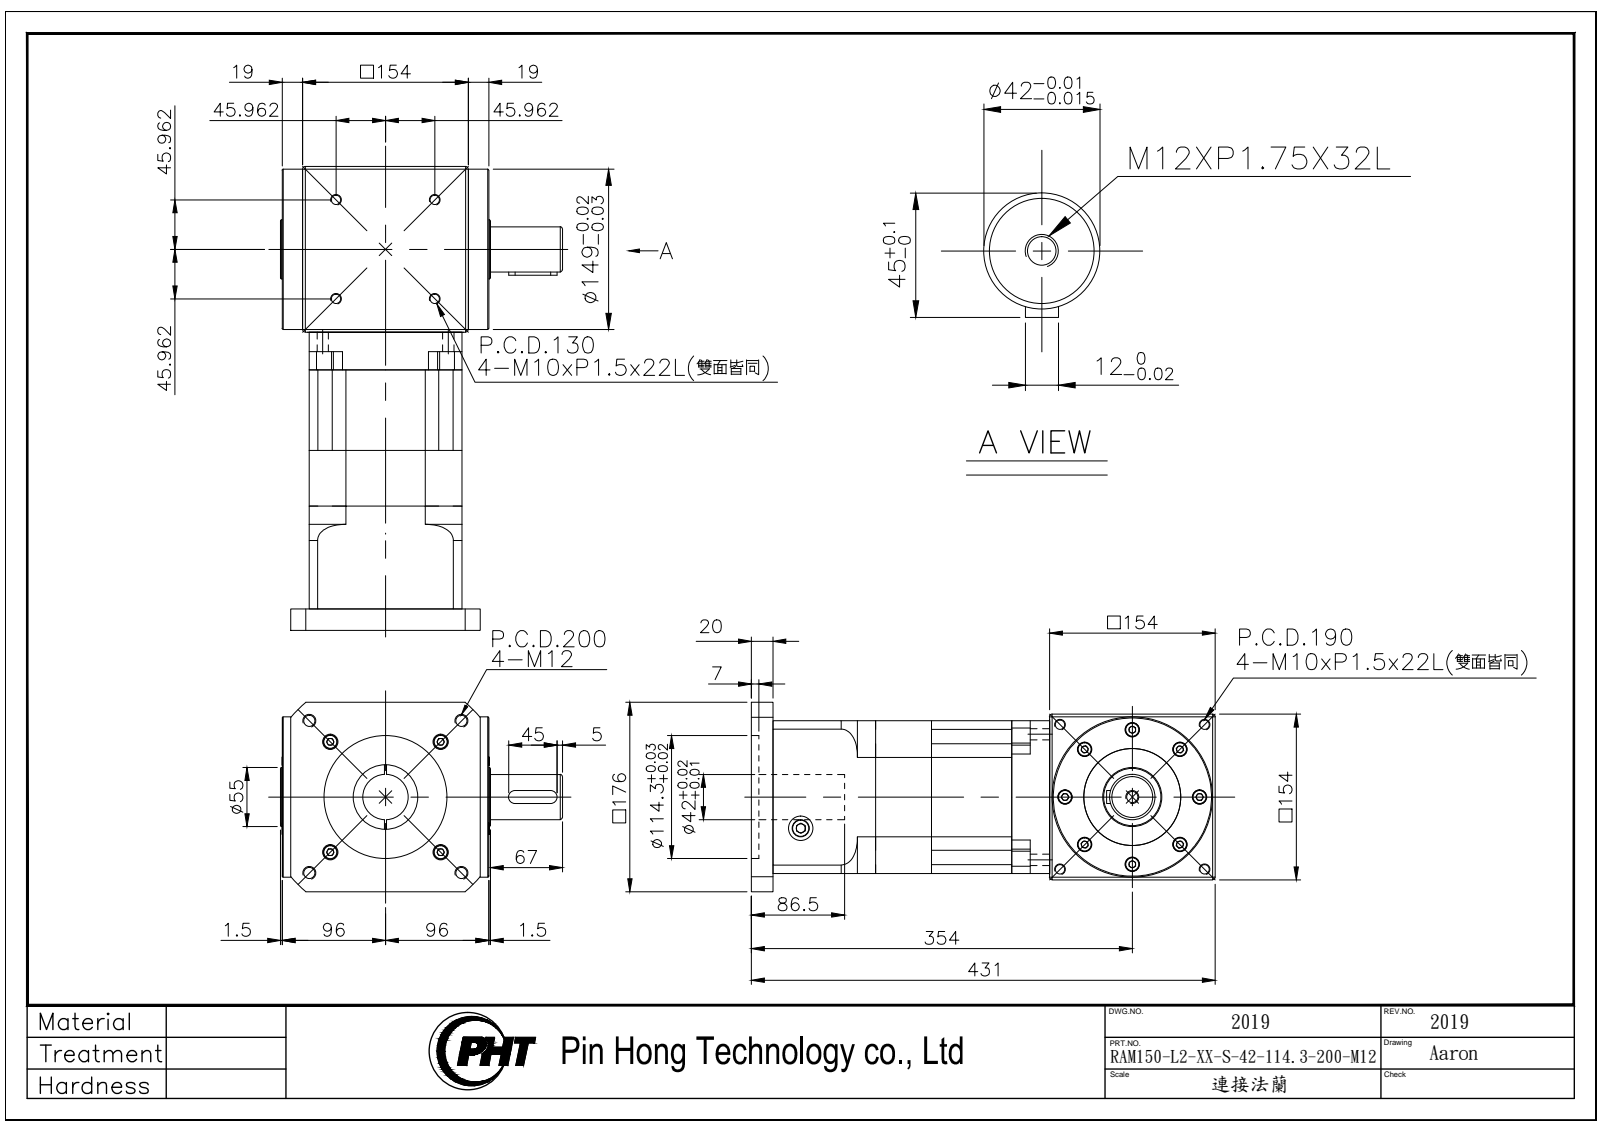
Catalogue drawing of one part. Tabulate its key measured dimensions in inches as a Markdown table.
| quantity | value |
| --- | --- |
| part name | RAM150-L2-XX-S-42-114.3-200-M12_2019 |
| STEP written by | SolidWorks 2016 (AUTOMOTIVE_DESIGN) |
| units | inches |
| bodies | 6 solids, 903 faces (422 planar, 321 cylindrical, 160 other) |
| overall size | 16.969 × 10.315 × 6.929 |
| volume | 569.6 in³ |
| surface area | 989.2 in² |
| round holes (diameter × count) | 0.335 × 12, 0.354 × 12, 0.551 × 12, 0.433 × 8, 0.689 × 8, 0.402 × 5, 0.268 × 4, 0.413 × 4, 0.886 × 2, 0.161 × 1, 1.654 × 1, 2.362 × 1 |
| round bosses / shafts (diameter × count) | 0.63 × 12, 0.512 × 4, 5.866 × 1, 5.118 × 1, 3.543 × 1, 2.913 × 1, 2.165 × 1, 1.654 × 1 |
| partial cylindrical surfaces (radius × count) | 0.394 × 4, 0.236 × 2, 3.15 × 1, 3.74 × 1, 4.228 × 1, 4.528 × 1 |
| main face-to-face distances | 0.236, 5.827, 6.063, 5.591, 2.039, 4.98, 2.941, 6.358, 4.319, 1.378 |
| hole center spacings | 2.795, 0.737, 0.74, 0.908, 1.433, 1.883, 2.651, 3.265 |
